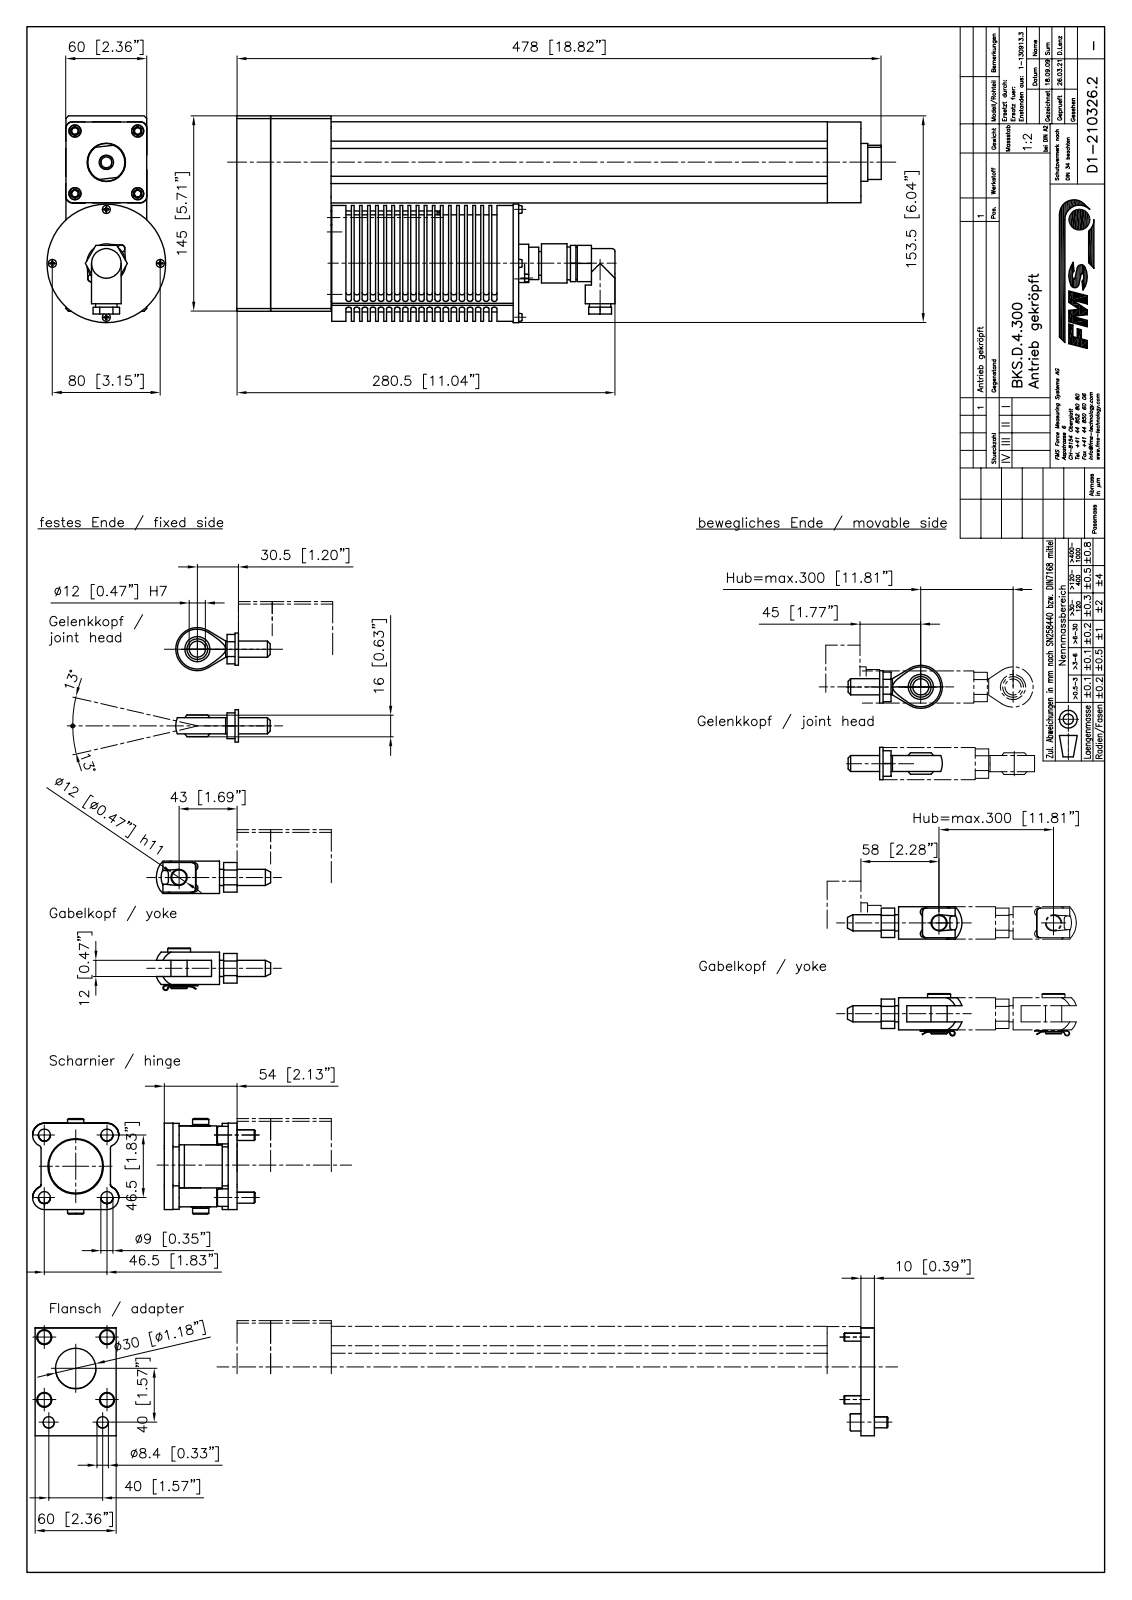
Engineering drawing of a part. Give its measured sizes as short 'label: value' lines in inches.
name: K2103262_STP; K1309121; K0702222; K0909182 (+8 more)
written by: Mechanical Desktop 2009 (CONFIG_CONTROL_DESIGN)
unit: in
bodies: 33 solids, 1467 faces (714 planar, 565 cylindrical, 188 other)
size: 22.48 × 6.043 × 3.465
volume: 97.94 in³; area: 890.9 in²
holes: 10× ⌀0.102, 8× ⌀0.135, 8× ⌀0.203, 5× ⌀0.197, 4× ⌀0.157, 4× ⌀0.248, 4× ⌀0.252, 4× ⌀0.262, 4× ⌀0.272, 4× ⌀0.354, 3× ⌀0.084, 2× ⌀0.142
bosses: 7× ⌀0.085, 6× ⌀0.118, 4× ⌀0.394, 4× ⌀0.236, 2× ⌀0.945, 2× ⌀0.217, 1× ⌀3.465, 1× ⌀3.386
rounds: 82× R0.079, 19× R0.197, 14× R0.02, 8× R0.315, 6× R0.118, 5× R0.787, 4× R0.069, 4× R0.177
face distances: 2.374, 2.368, 2.362, 0.077, 2.297, 0.071, 2.291, 0.209, 2.165, 2.22
hole spacings: 1.131, 2.668, 1.294, 1.174, 1.311, 1.563, 1.575, 1.67
